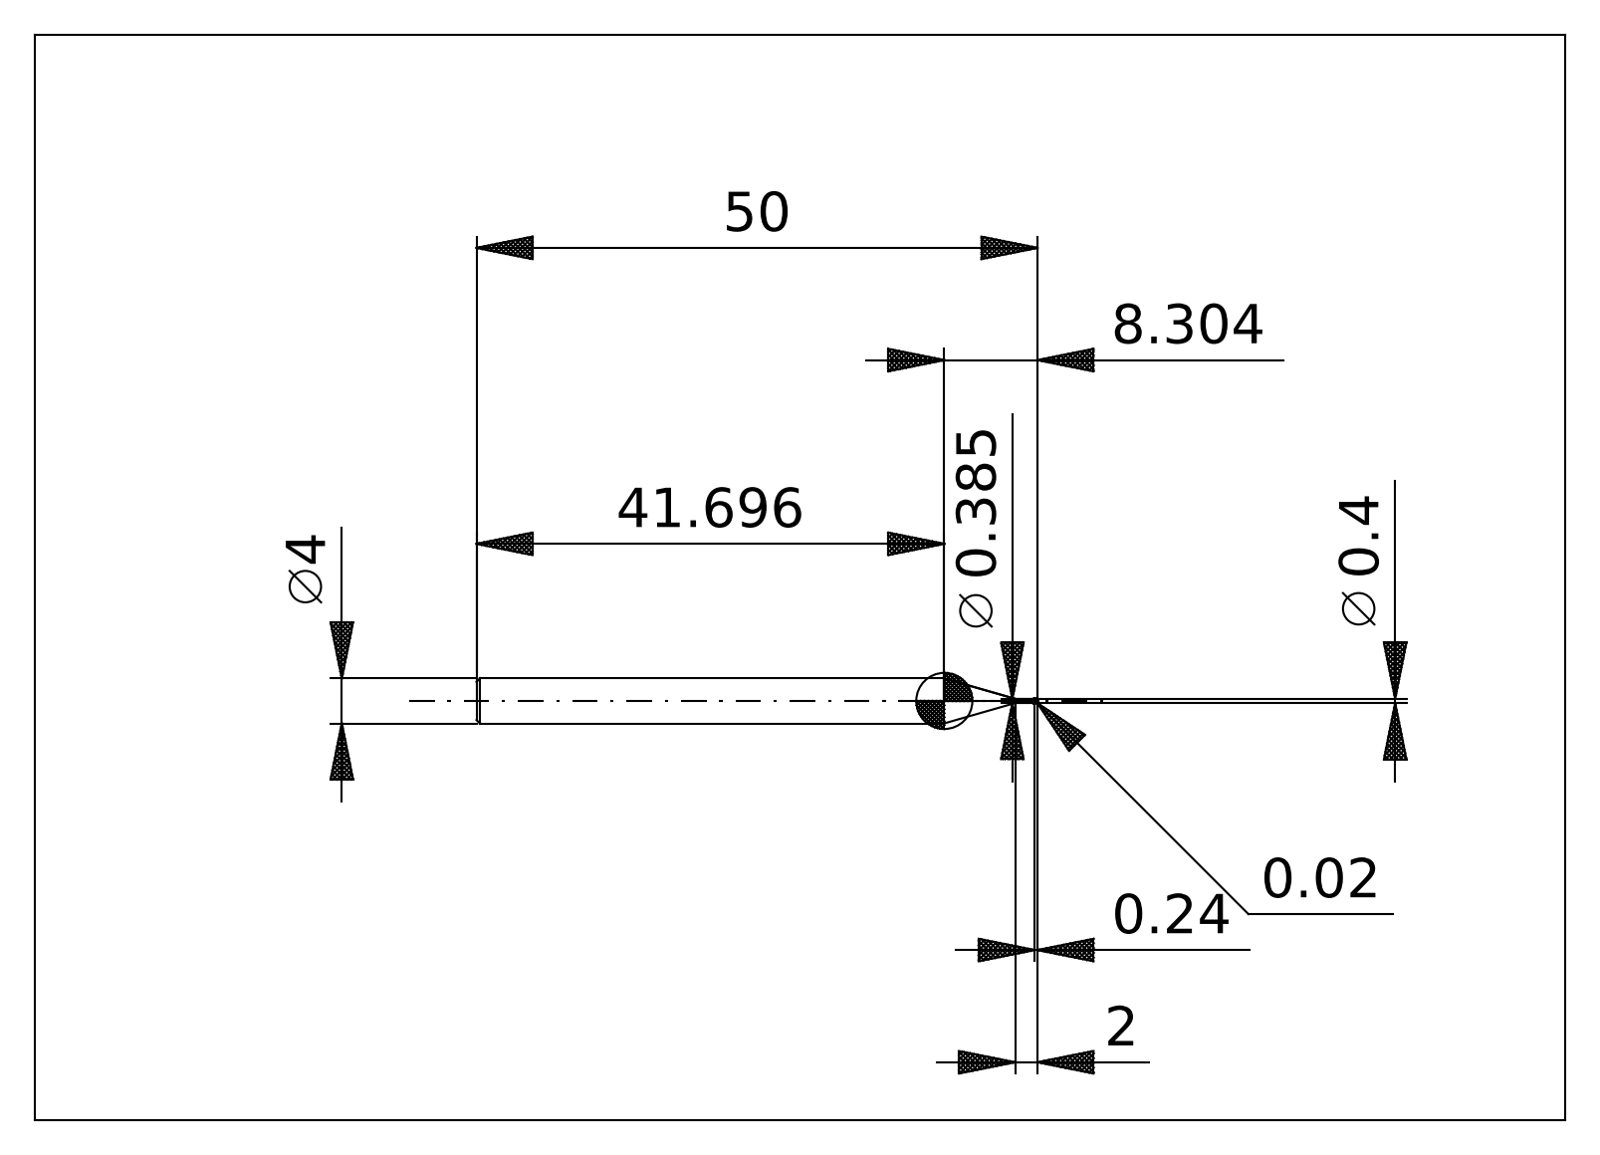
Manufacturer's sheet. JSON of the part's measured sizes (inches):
{"step_written_by": "ACIS (automotive_design)", "units": "inches", "bodies": {"solids": 2, "faces": 26, "planar": 6, "cylindrical": 8, "other": 12}, "overall_size": [1.969, 0.157, 0.157], "volume_in3": 0.034, "surface_area_in2": 0.902, "round_bosses_or_shafts": [[0.157, 1], [0.015, 1]], "face_to_face_distances": [1.969, 1.966, 1.959, 0.327, 0.324, 0.317, 1.642]}
